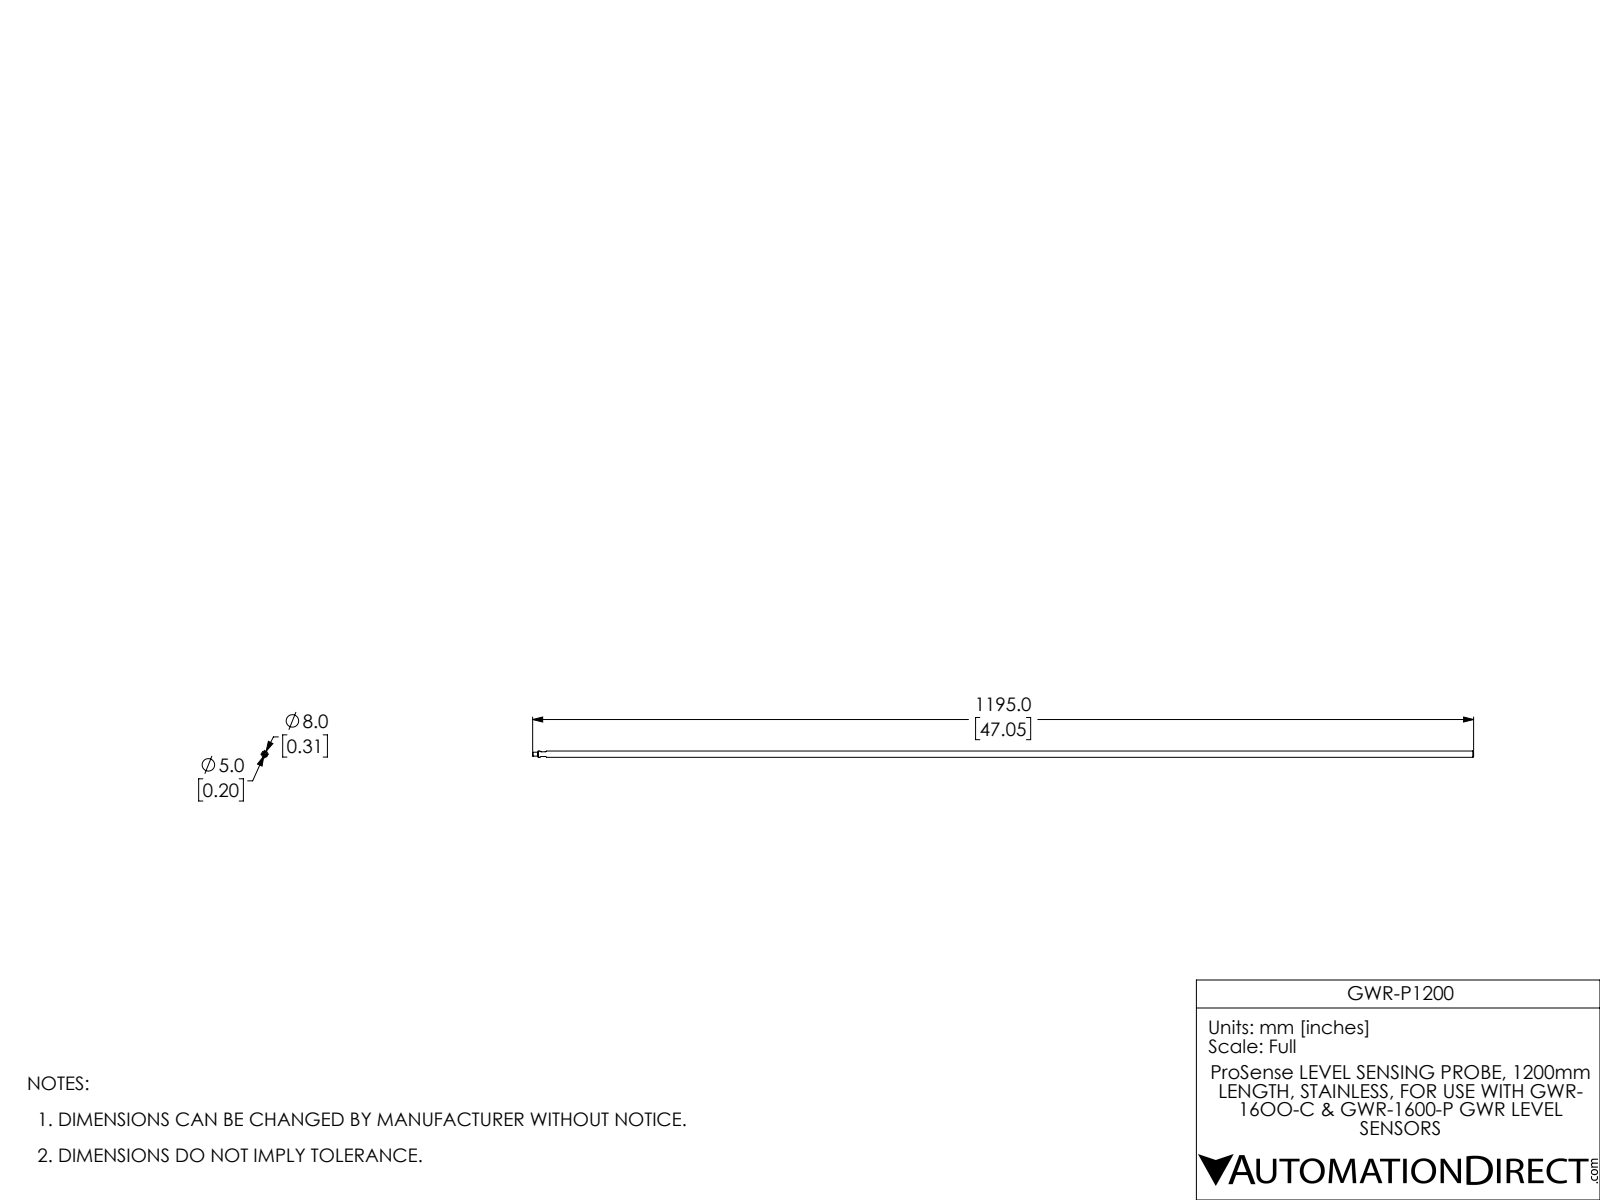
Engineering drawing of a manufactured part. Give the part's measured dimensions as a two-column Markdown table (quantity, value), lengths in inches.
| quantity | value |
| --- | --- |
| part name | GWR-P1200 |
| STEP written by | SolidWorks 2017 (AUTOMOTIVE_DESIGN) |
| units | inches |
| bodies | 1 solid, 19 faces (5 planar, 8 cylindrical, 6 other) |
| overall size | 47.047 × 0.315 × 0.315 |
| volume | 3.648 in³ |
| surface area | 46.58 in² |
| round bosses / shafts (diameter × count) | 0.315 × 1, 0.197 × 1 |
| partial cylindrical surfaces (radius × count) | 0.079 × 4 |
| main face-to-face distances | 46.772, 0.236, 47.047, 0.276 |
